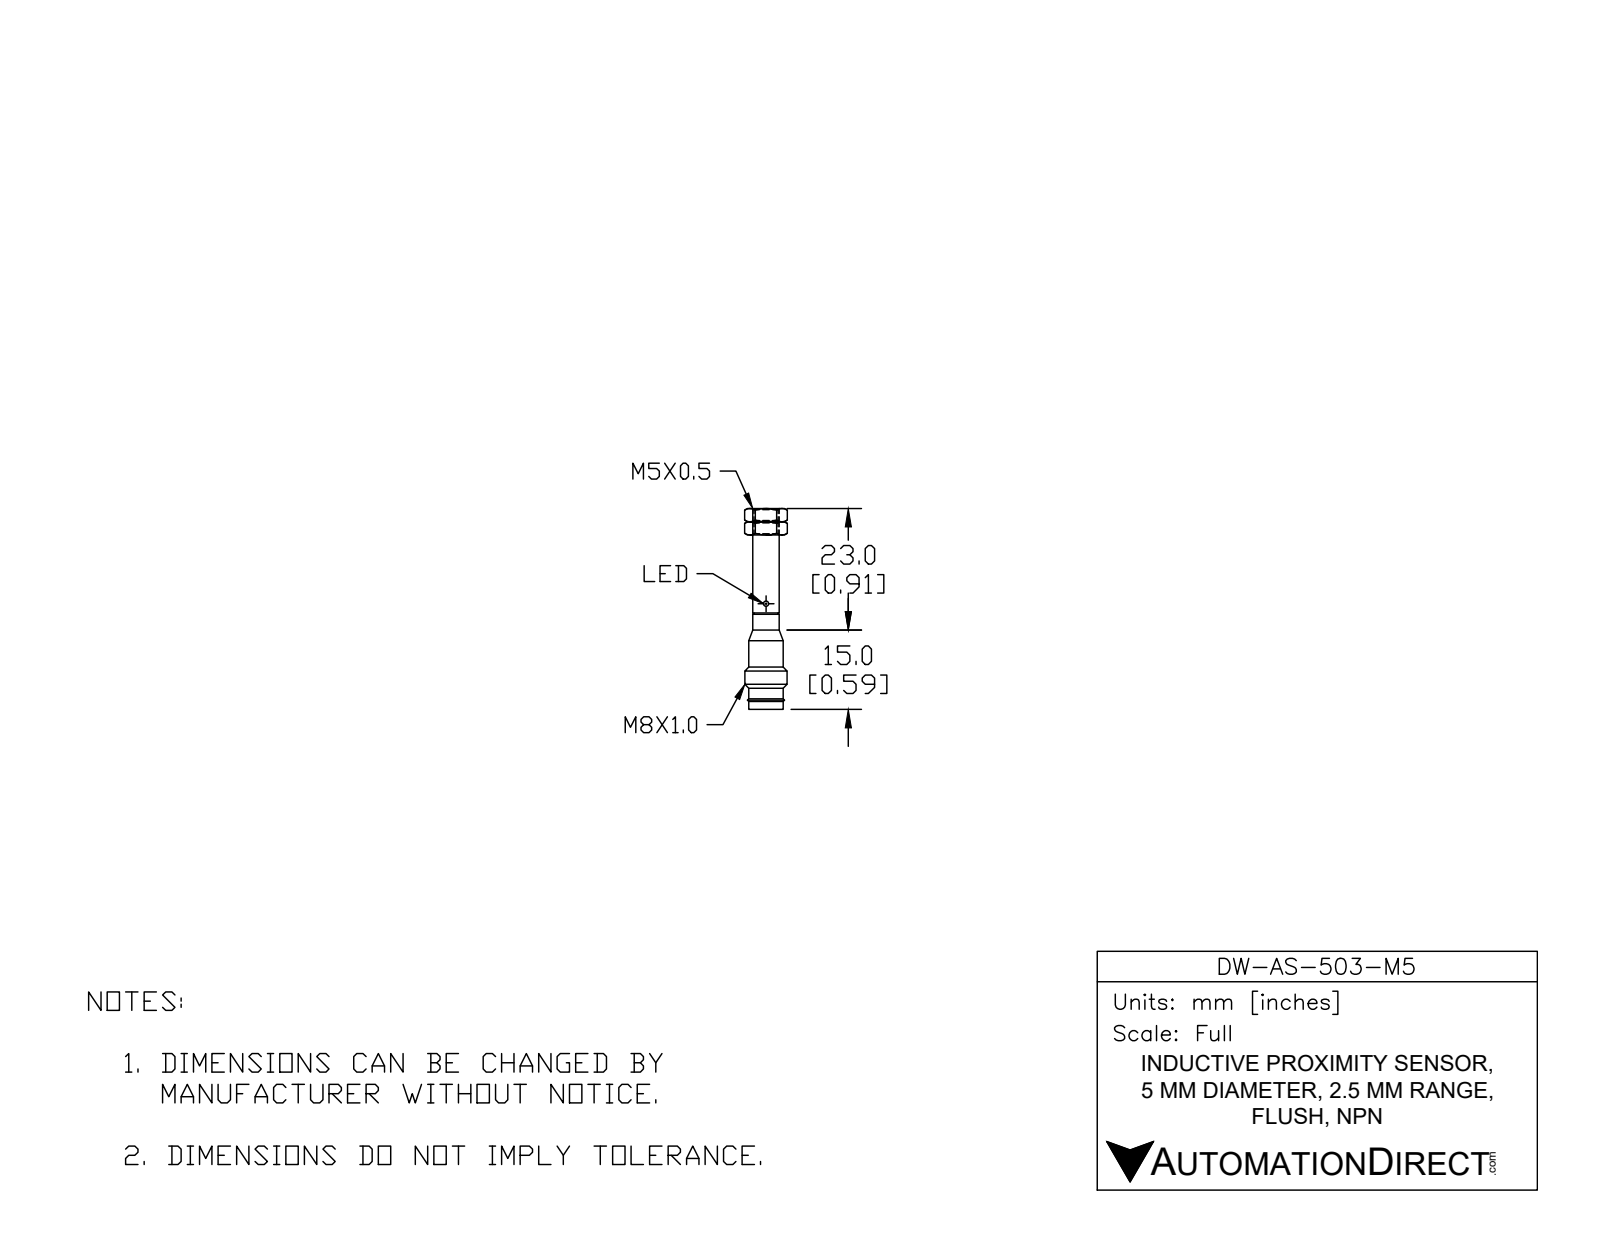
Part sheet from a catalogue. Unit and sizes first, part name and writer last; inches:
Units: inches
Overall size (bounding box): 1.496 × 0.315 × 0.315
Round holes (diameter × count): ⌀0.059 ×1, ⌀0.14 ×1, ⌀0.217 ×1, ⌀0.228 ×1
Round bosses / shafts (diameter × count): ⌀0.039 ×3, ⌀0.315 ×1, ⌀0.272 ×1, ⌀0.256 ×1, ⌀0.228 ×1, ⌀0.197 ×1, ⌀0.132 ×1
Main face-to-face distances: 0.03, 1.269, 1.299, 1.267, 1.297, 0.051, 0.049, 1.218, 1.248, 0.047
Volume: 0.026 in³ · Surface area: 2.173 in²
Bodies: 4 solids, 42 faces (11 planar, 15 cylindrical, 16 other)
Part name (STEP PRODUCT): DW-AS-503-M5
STEP written by: SolidWorks 2017 (AUTOMOTIVE_DESIGN)
